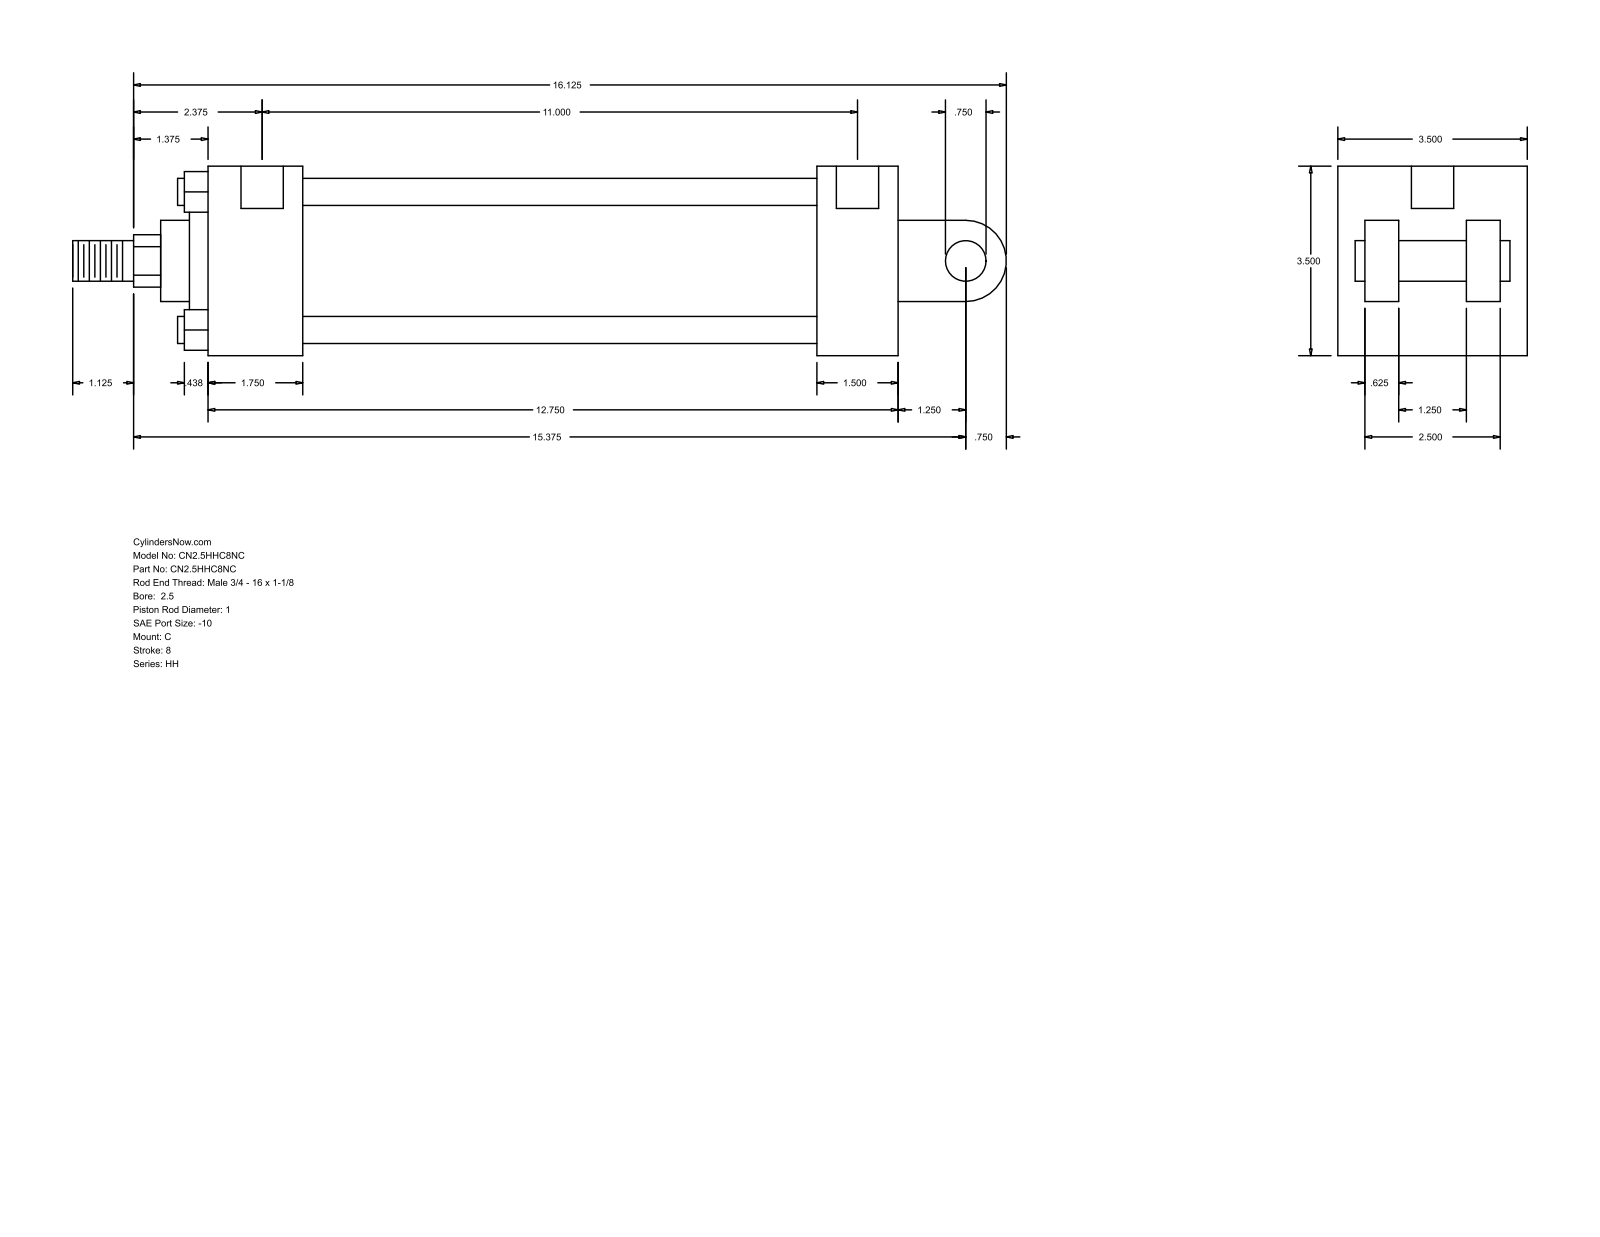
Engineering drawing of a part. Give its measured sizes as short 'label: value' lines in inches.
name: HH_C__0250_1
written by: GSSL Pune (CONFIG_CONTROL_DESIGN)
unit: in
bodies: 0 solids, 101 faces (71 planar, 30 cylindrical, 0 other)
size: 17.25 × 3.5 × 3.5
holes: 4× ⌀0.219, 2× ⌀0.781
bosses: 4× ⌀0.5, 2× ⌀0.75, 1× ⌀2.875, 1× ⌀2.375, 1× ⌀1.5, 1× ⌀1
rounds: 1× R0.484, 1× R0.75
face distances: 3.5, 12.75, 2.5, 11.25, 1.5, 1.75, 9.5, 11, 0.5, 1.125
hole spacings: 11.125, 0.062, 0.063, 11, 11.062, 11.063
